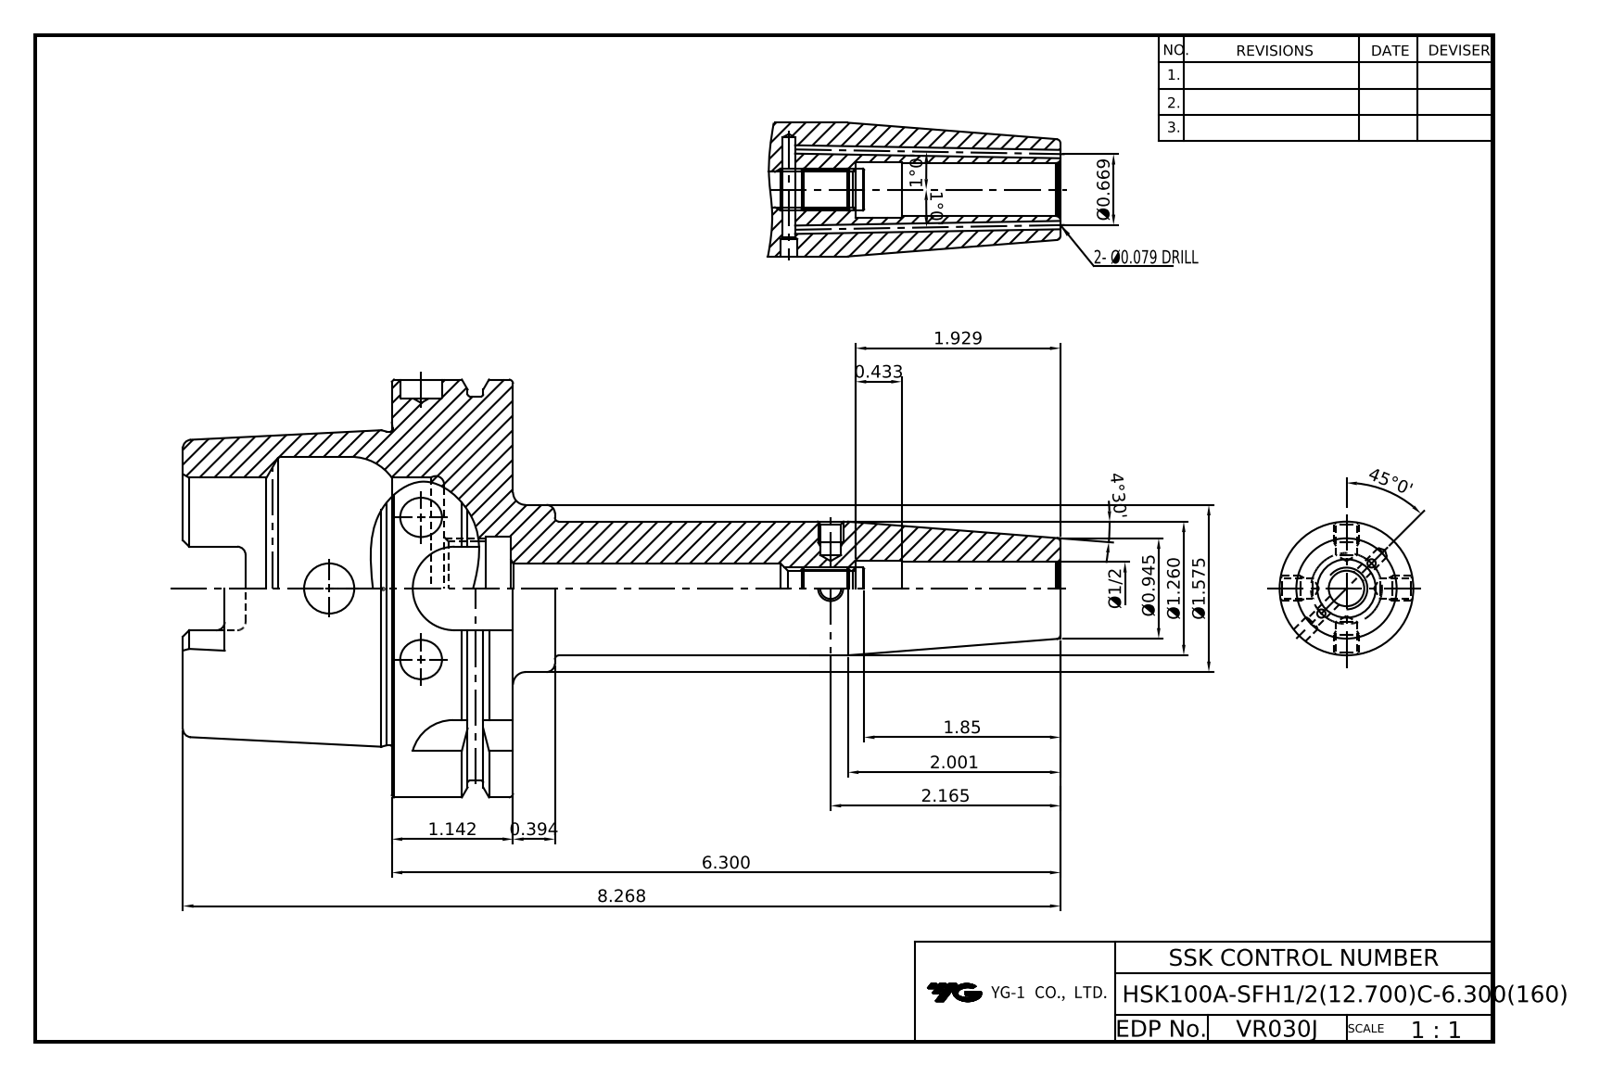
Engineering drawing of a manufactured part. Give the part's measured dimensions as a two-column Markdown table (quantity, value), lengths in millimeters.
| quantity | value |
| --- | --- |
| part name | LO-HSK100A-SFH12.7C-160 |
| STEP written by | Autodesk Inventor 2022 (AUTOMOTIVE_DESIGN) |
| units | millimeters |
| bodies | 1 solid, 123 faces (39 planar, 38 cylindrical, 46 other) |
| overall size | 210 × 100 × 100 |
| volume | 339 513 mm³ |
| surface area | 67 453 mm² |
| round holes (diameter × count) | 2 × 2, 12 × 2, 8.92 × 1, 10 × 1, 12.7 × 1, 13.9 × 1, 22.38 × 1, 25 × 1, 53 × 1, 63 × 1 |
| round bosses / shafts (diameter × count) | 100 × 1, 92 × 1, 75.41 × 1, 40 × 1, 32 × 1 |
| partial cylindrical surfaces (radius × count) | 2 × 6, 4.88 × 4, 10 × 4 |
| main face-to-face distances | 29, 12.5, 16.5, 79, 62.5, 50, 88, 10, 78.5, 28.5 |
